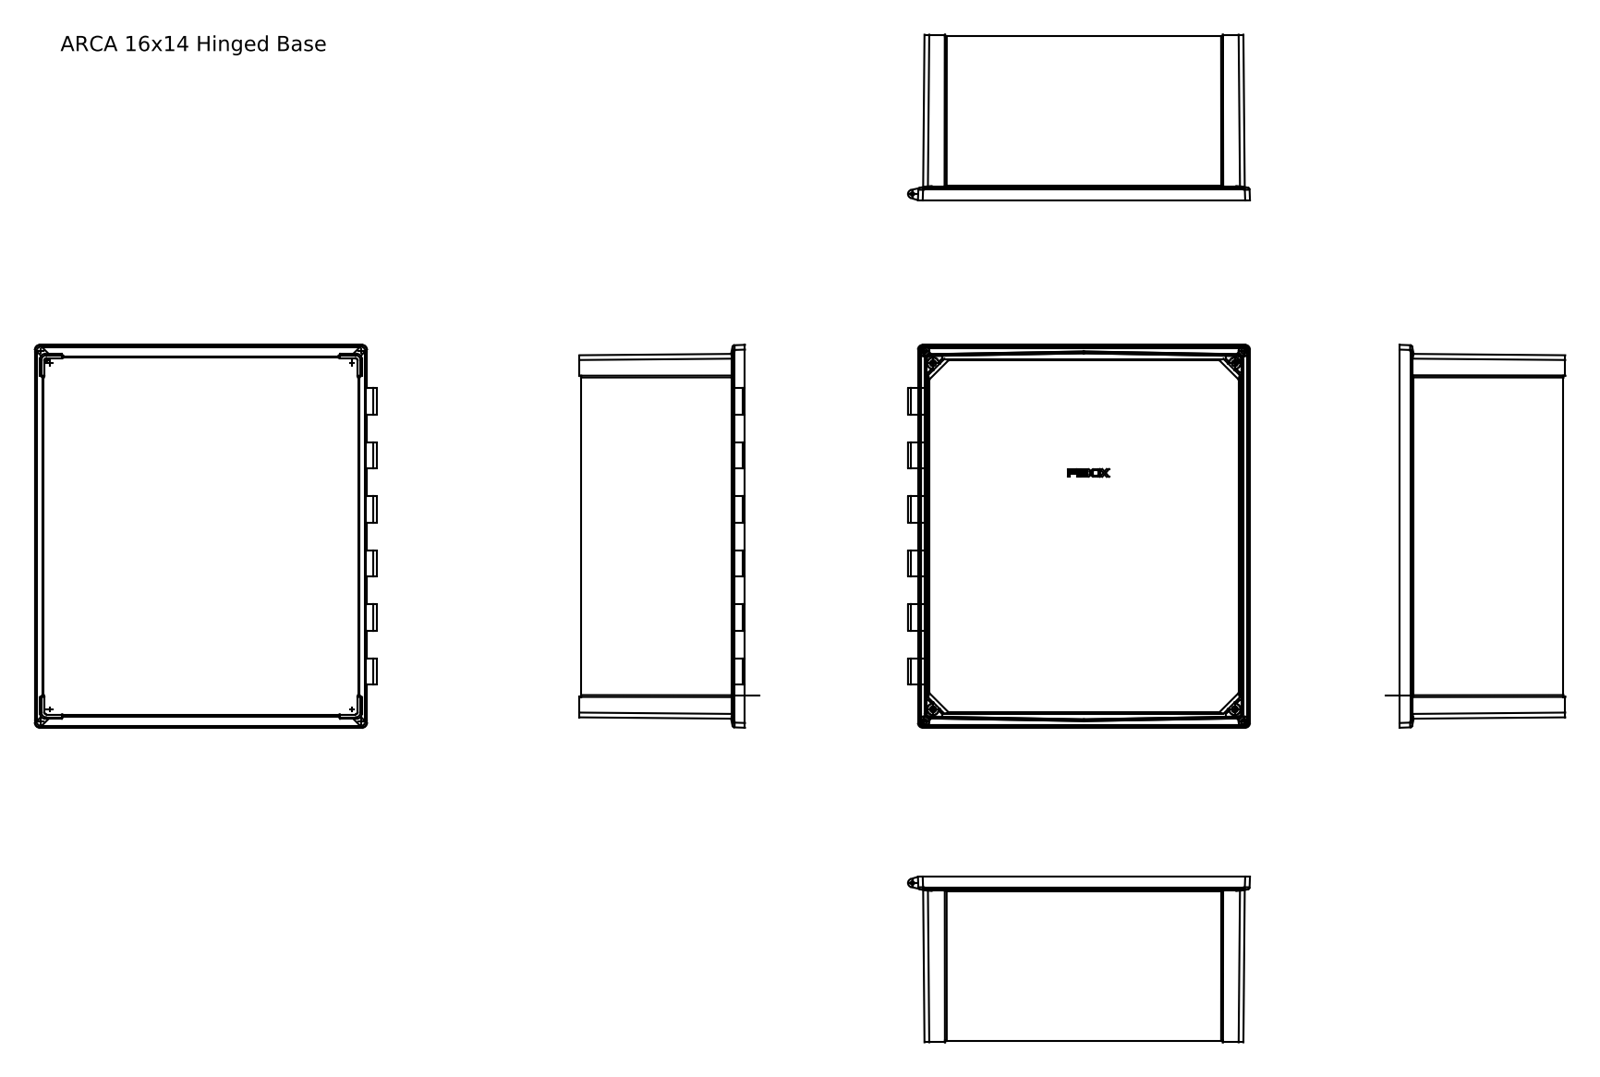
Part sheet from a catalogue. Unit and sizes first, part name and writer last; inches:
Units: inches
Overall size (bounding box): 17.437 × 15.571 × 7.535
Round holes (diameter × count): ⌀0.15 ×1
Partial cylindrical surfaces — rounded edges, fillets, slot ends (radius × count): R0.217 ×12, R0.101 ×6, R0.038 ×4, R0.098 ×4, R0.138 ×4, R0.886 ×4, R1.043 ×4, R0.041 ×2
Main face-to-face distances: 0.126, 0.142, 0.102, 0.228, 0.118, 0.16, 0.058, 0.068, 0.157, 14.57
Volume: 109.5 in³ · Surface area: 1 470 in²
Bodies: 6 solids, 500 faces (294 planar, 68 cylindrical, 138 other)
Part name (STEP PRODUCT): 16x14_hinge_base
STEP written by: SolidWorks 2015 (AUTOMOTIVE_DESIGN)
